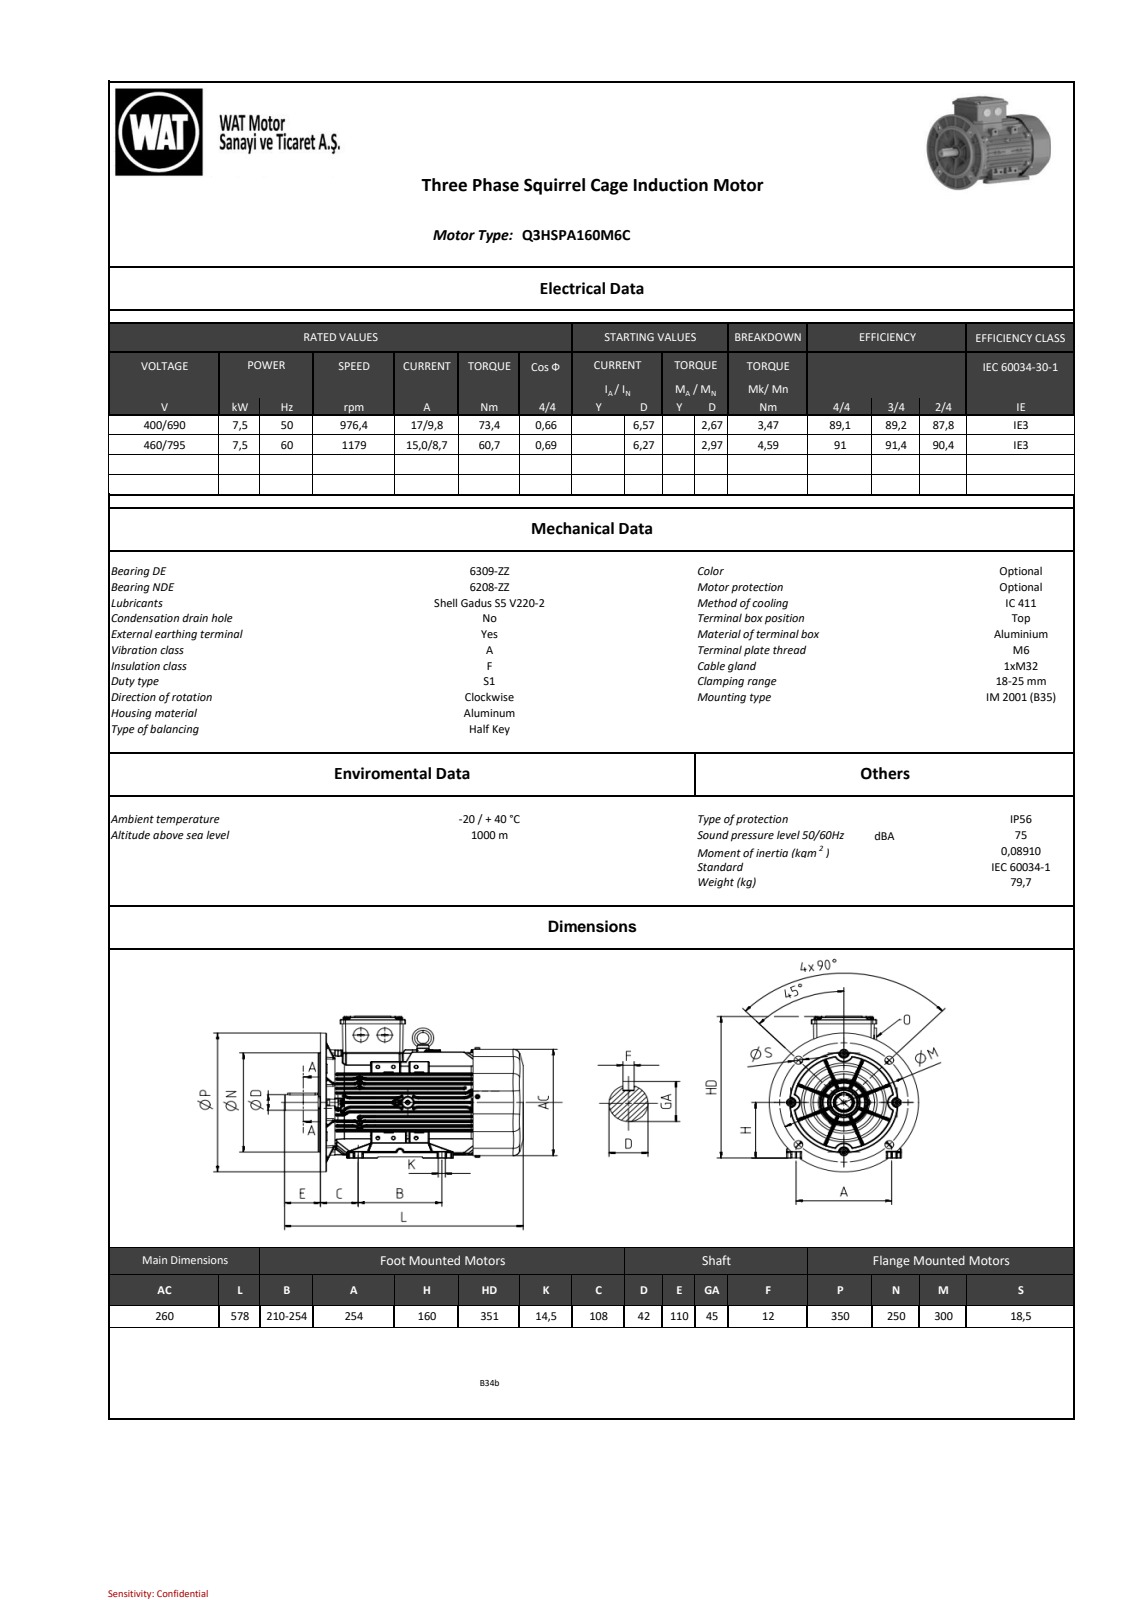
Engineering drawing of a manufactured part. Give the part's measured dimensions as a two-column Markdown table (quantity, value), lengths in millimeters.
| quantity | value |
| --- | --- |
| part name | QHS series_ 160_B35 _DEEP COVER__stp_objects |
| STEP written by | SIEMENS PLM Software NX2206.8101 (AP203_CONFIGURATION_CONTROLLED_3D_DESIGN_OF_MECHANICAL_PARTS_AND_ASSEMBLIES_MIM_LF) |
| units | millimeters |
| bodies | 0 solids, 8321 faces (2019 planar, 3628 cylindrical, 2674 other) |
| overall size | 579 × 365.15 × 349.89 |
| round holes (diameter × count) | 17 × 5, 4.6 × 2, 8.48 × 2, 16 × 1, 62 × 1, 68.67 × 1, 82 × 1, 180 × 1, 223 × 1 |
| round bosses / shafts (diameter × count) | 13 × 4, 8 × 4, 38 × 2, 250 × 1, 230.5 × 1, 86.77 × 1, 45 × 1, 42 × 1 |
| partial cylindrical surfaces (radius × count) | 1 × 1039, 0.8 × 877, 2 × 219, 3 × 78, 1.5 × 66, 0.5 × 51, 7 × 48, 5 × 32 |
| main face-to-face distances | 1.5, 10.42, 10.56, 14, 4, 10.28, 7, 20.84, 125.58, 94.46 |
| hole center spacings | 120.5, 170.41, 241, 143 |
